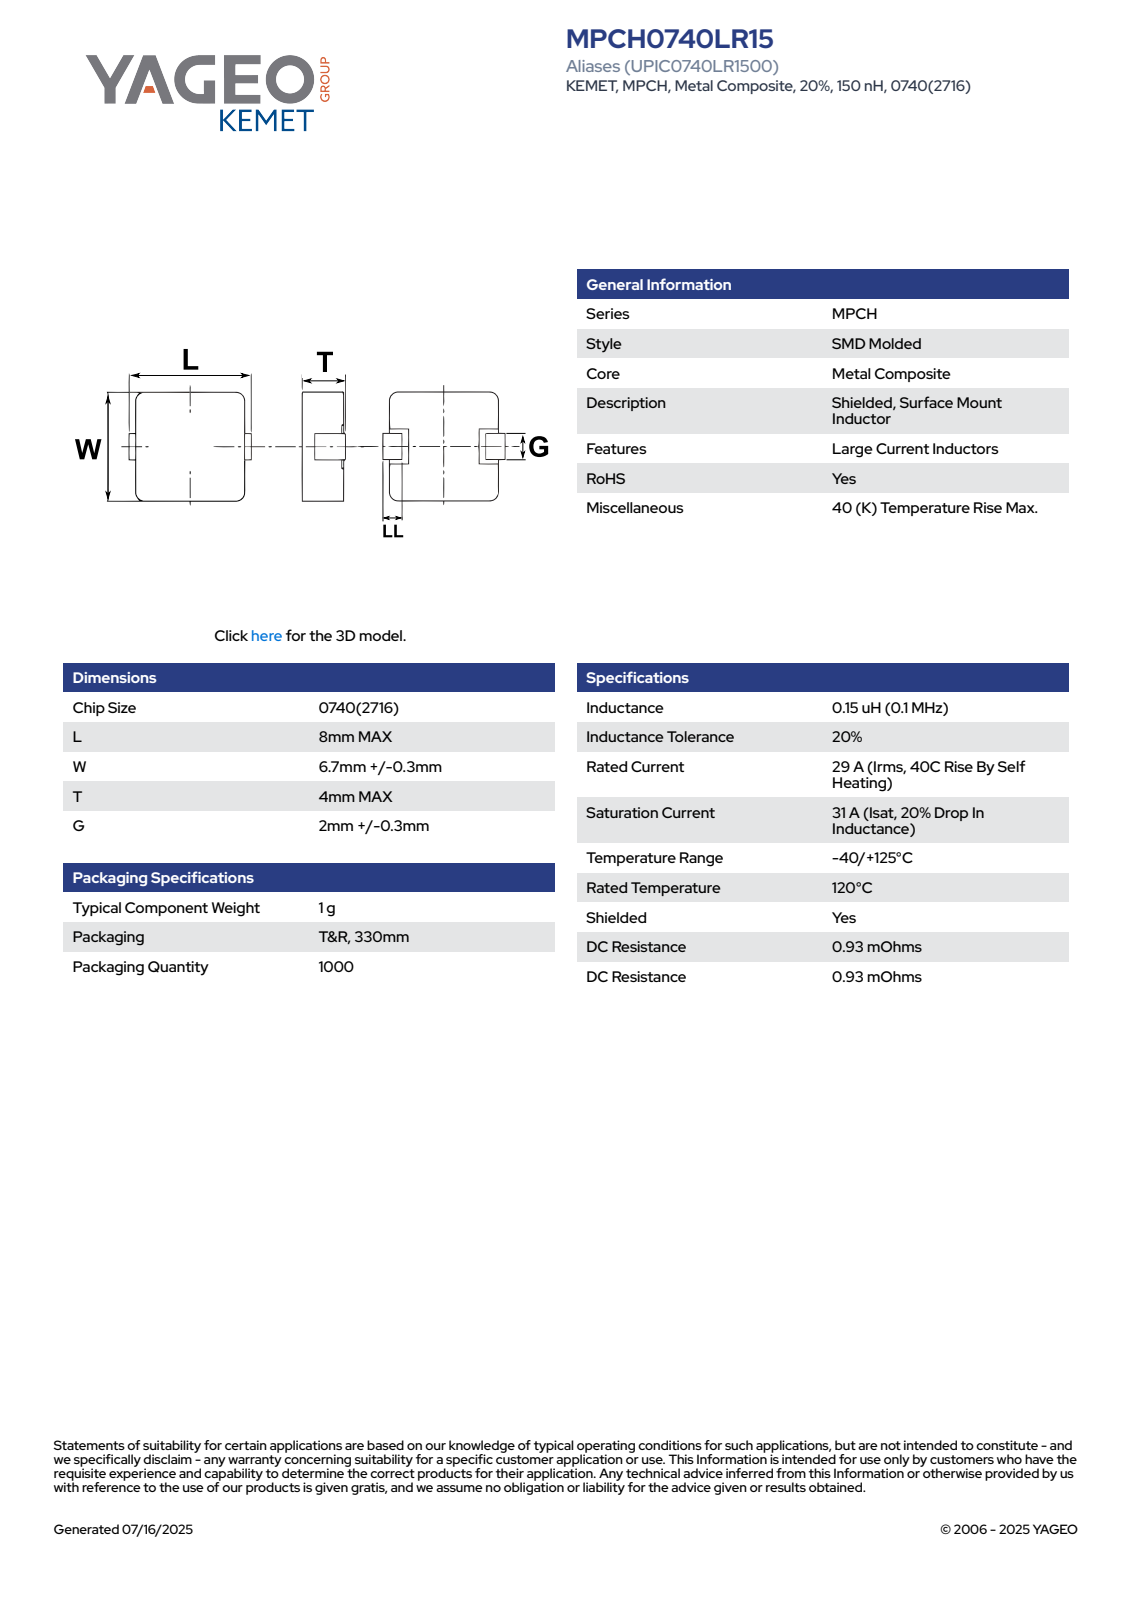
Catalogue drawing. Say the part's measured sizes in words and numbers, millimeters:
The part is named "IS_MPC_3126_L8W7T4LL1.5G2.3". Its 3-D file was written by "SolidWorks 2014 (AUTOMOTIVE_DESIGN)". It is 4 solids with 105 faces: 93 planar, 12 cylindrical and 0 other. Overall it measures 8 by 7 by 4 millimeters. Its volume is 210 cubic millimeters and its surface area 250 square millimeters. Partial cylindrical surfaces (rounded edges, fillets, slot ends): 4 of radius 0.6. The main face-to-face distances are 3.95, 7, 7.59, 7.8, 7.58, 7.6, 7.79, 7.9, 7.69, 7.7.
